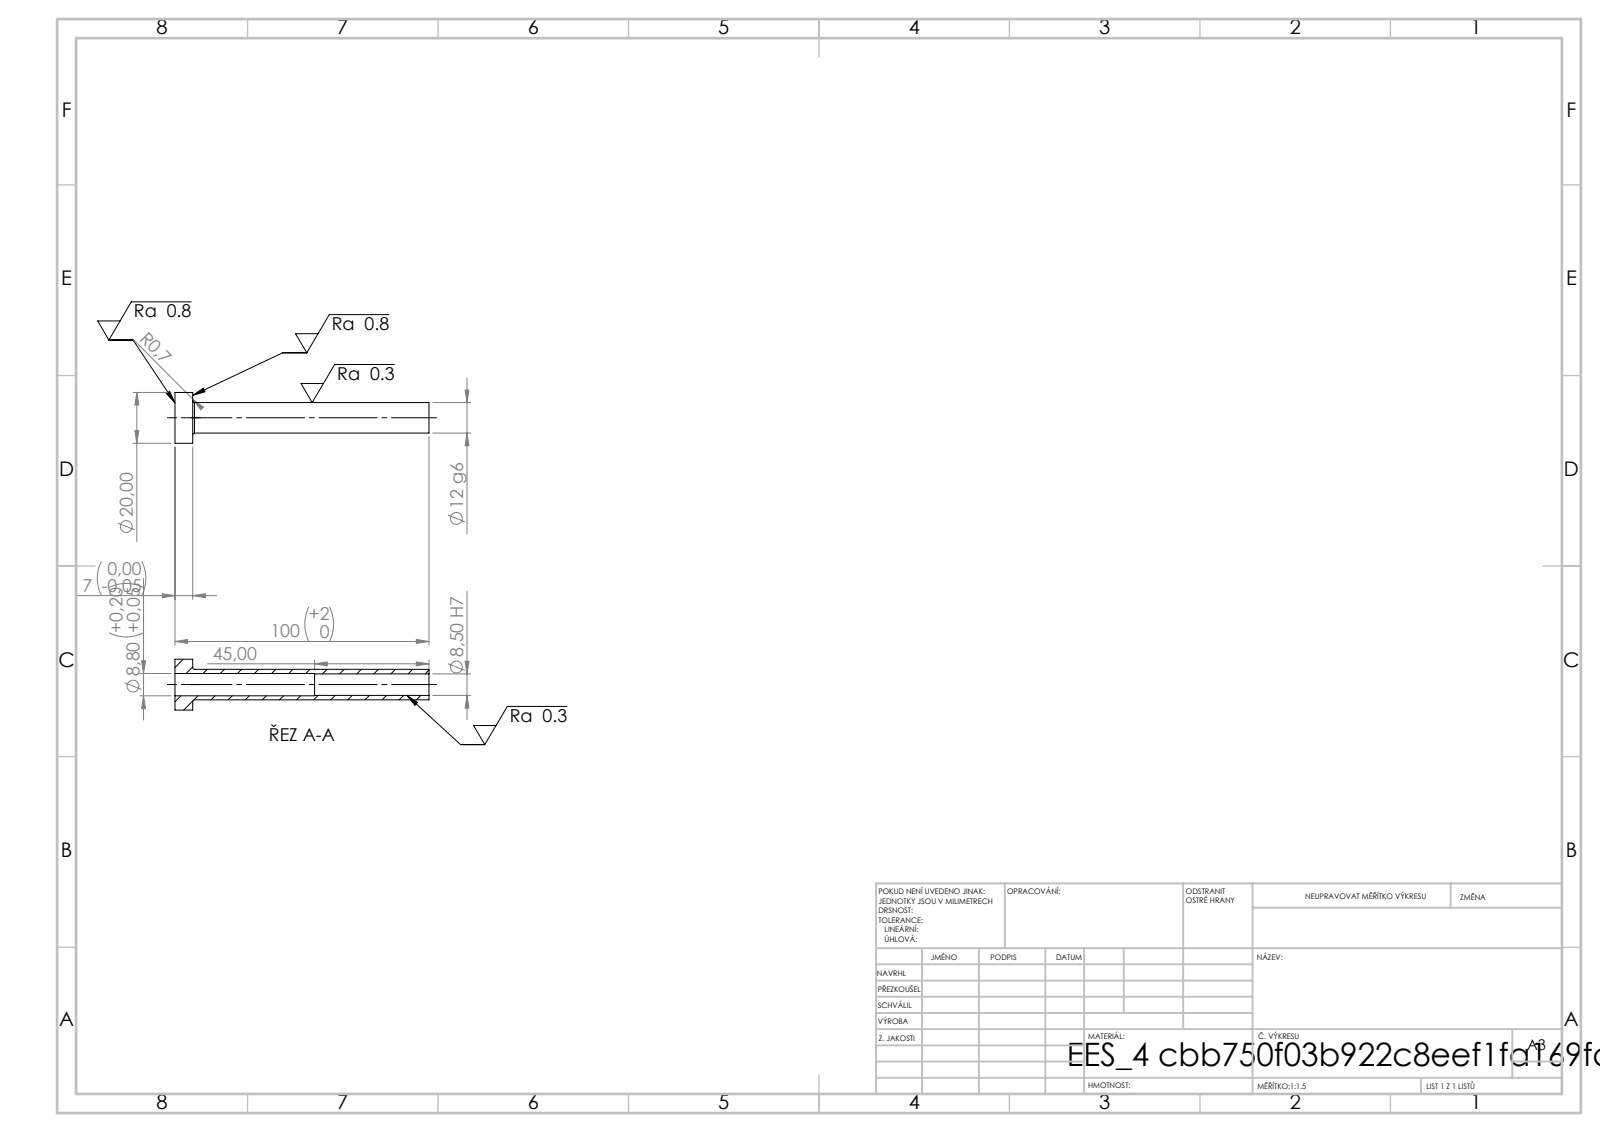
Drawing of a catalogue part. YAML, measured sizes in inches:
step_written_by: "SolidWorks 2019 (CONFIG_CONTROL_DESIGN)"
units: inches
bodies: {solids: 1, faces: 14, planar: 4, cylindrical: 8, other: 2}
overall_size: [3.937, 0.787, 0.787]
volume: 0.416
surface_area: 11.12
round_holes:
  - {diameter: 0.335, count: 1}
  - {diameter: 0.346, count: 1}
round_bosses_or_shafts:
  - {diameter: 0.787, count: 1}
  - {diameter: 0.472, count: 1}
face_to_face_distances: [0.276, 3.937, 3.661, 2.165, 1.89, 1.772]
